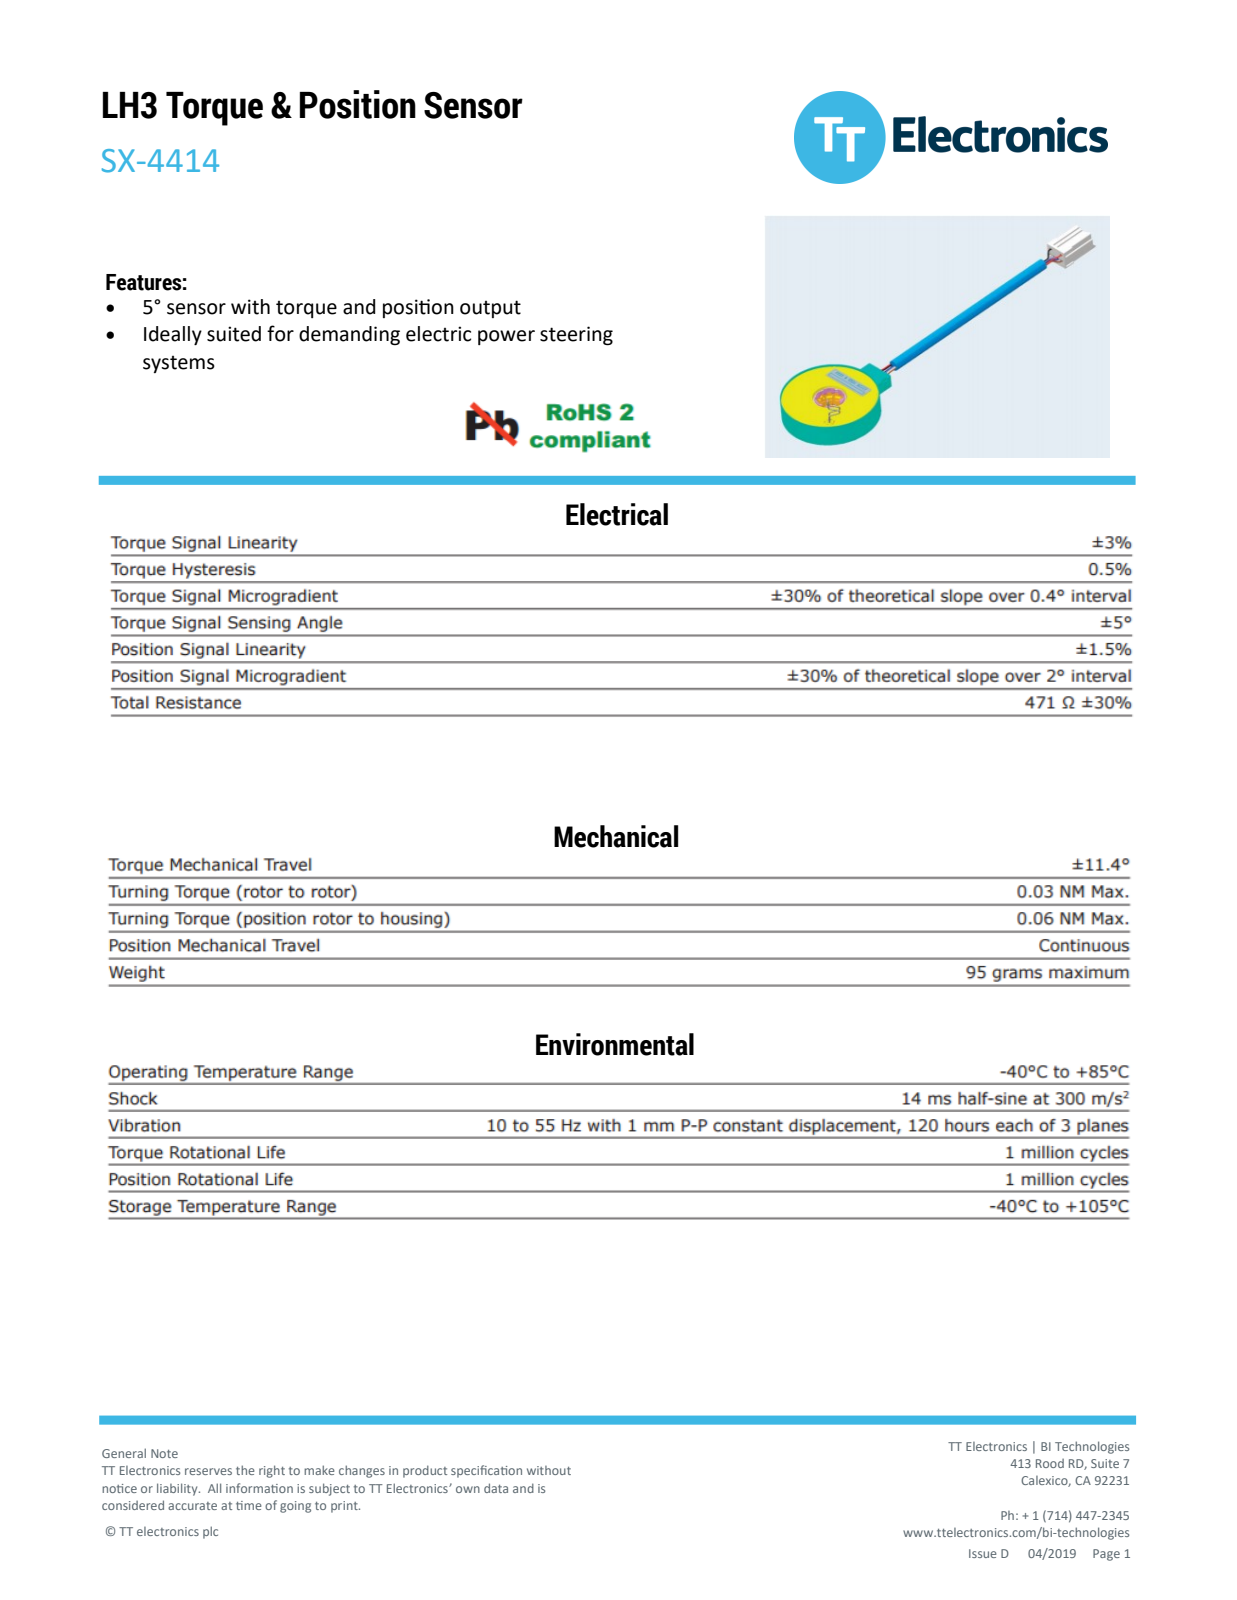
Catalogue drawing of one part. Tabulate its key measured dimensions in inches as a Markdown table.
| quantity | value |
| --- | --- |
| part name | SX-4414A_SW0001 |
| STEP written by | CREO PARAMETRIC BY PTC INC, 2014500 (CONFIG_CONTROL_DESIGN) |
| units | inches |
| bodies | 4 solids, 2477 faces (1303 planar, 837 cylindrical, 337 other) |
| overall size | 13.207 × 3.2 × 1.835 |
| volume | 5.862 in³ |
| surface area | 67.97 in² |
| round holes (diameter × count) | 0.02 × 6, 0.04 × 6, 0.985 × 1, 1.046 × 1, 1.126 × 1, 1.146 × 1, 1.241 × 1, 1.247 × 1, 1.255 × 1, 1.345 × 1, 2.57 × 1 |
| round bosses / shafts (diameter × count) | 0.062 × 18, 0.025 × 12, 0.094 × 6, 0.064 × 6, 0.047 × 6, 3.2 × 1, 1.24 × 1, 1.234 × 1 |
| partial cylindrical surfaces (radius × count) | 0.007 × 72, 0.012 × 72, 0.006 × 54, 0.01 × 54, 0.005 × 44, 0.02 × 33, 0.016 × 19, 0.028 × 18 |
| main face-to-face distances | 0.719, 0.05, 0.055, 0.669, 0.664, 0.06, 0.808, 0.521, 0.13, 0.144 |
| hole center spacings | 0.115, 0.23, 0.345, 0.46, 0.575, 0.23, 0.345, 0.69 |
